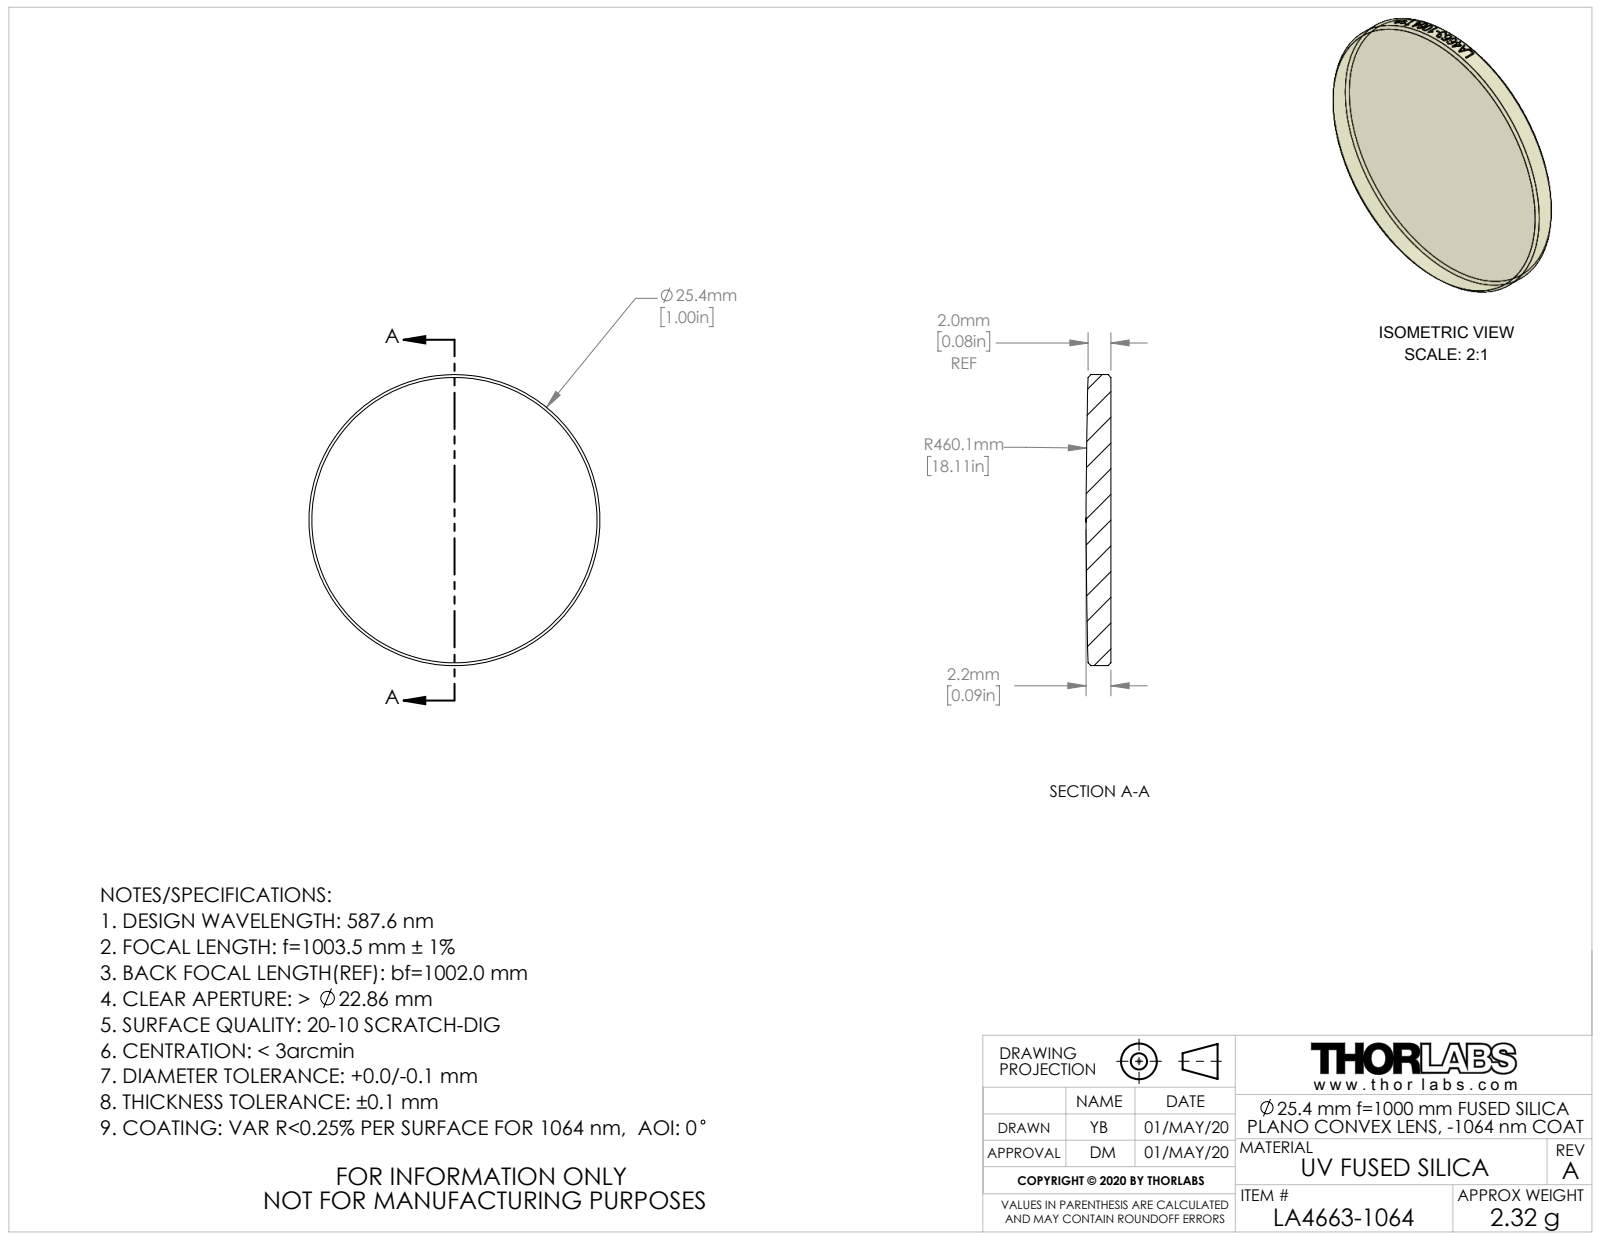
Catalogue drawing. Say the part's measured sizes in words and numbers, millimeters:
The part is named "CTN015552-E0W". Its 3-D file was written by "SolidWorks 2018 (AUTOMOTIVE_DESIGN)". It is 1 solid with 34 faces: 1 planar, 27 cylindrical and 6 other. Overall it measures 25.4 by 25.4 by 2.17 millimeters. Its volume is 1 052 cubic millimeters and its surface area 1 150 square millimeters. Round bosses or shafts: 1 of diameter 25.4.
